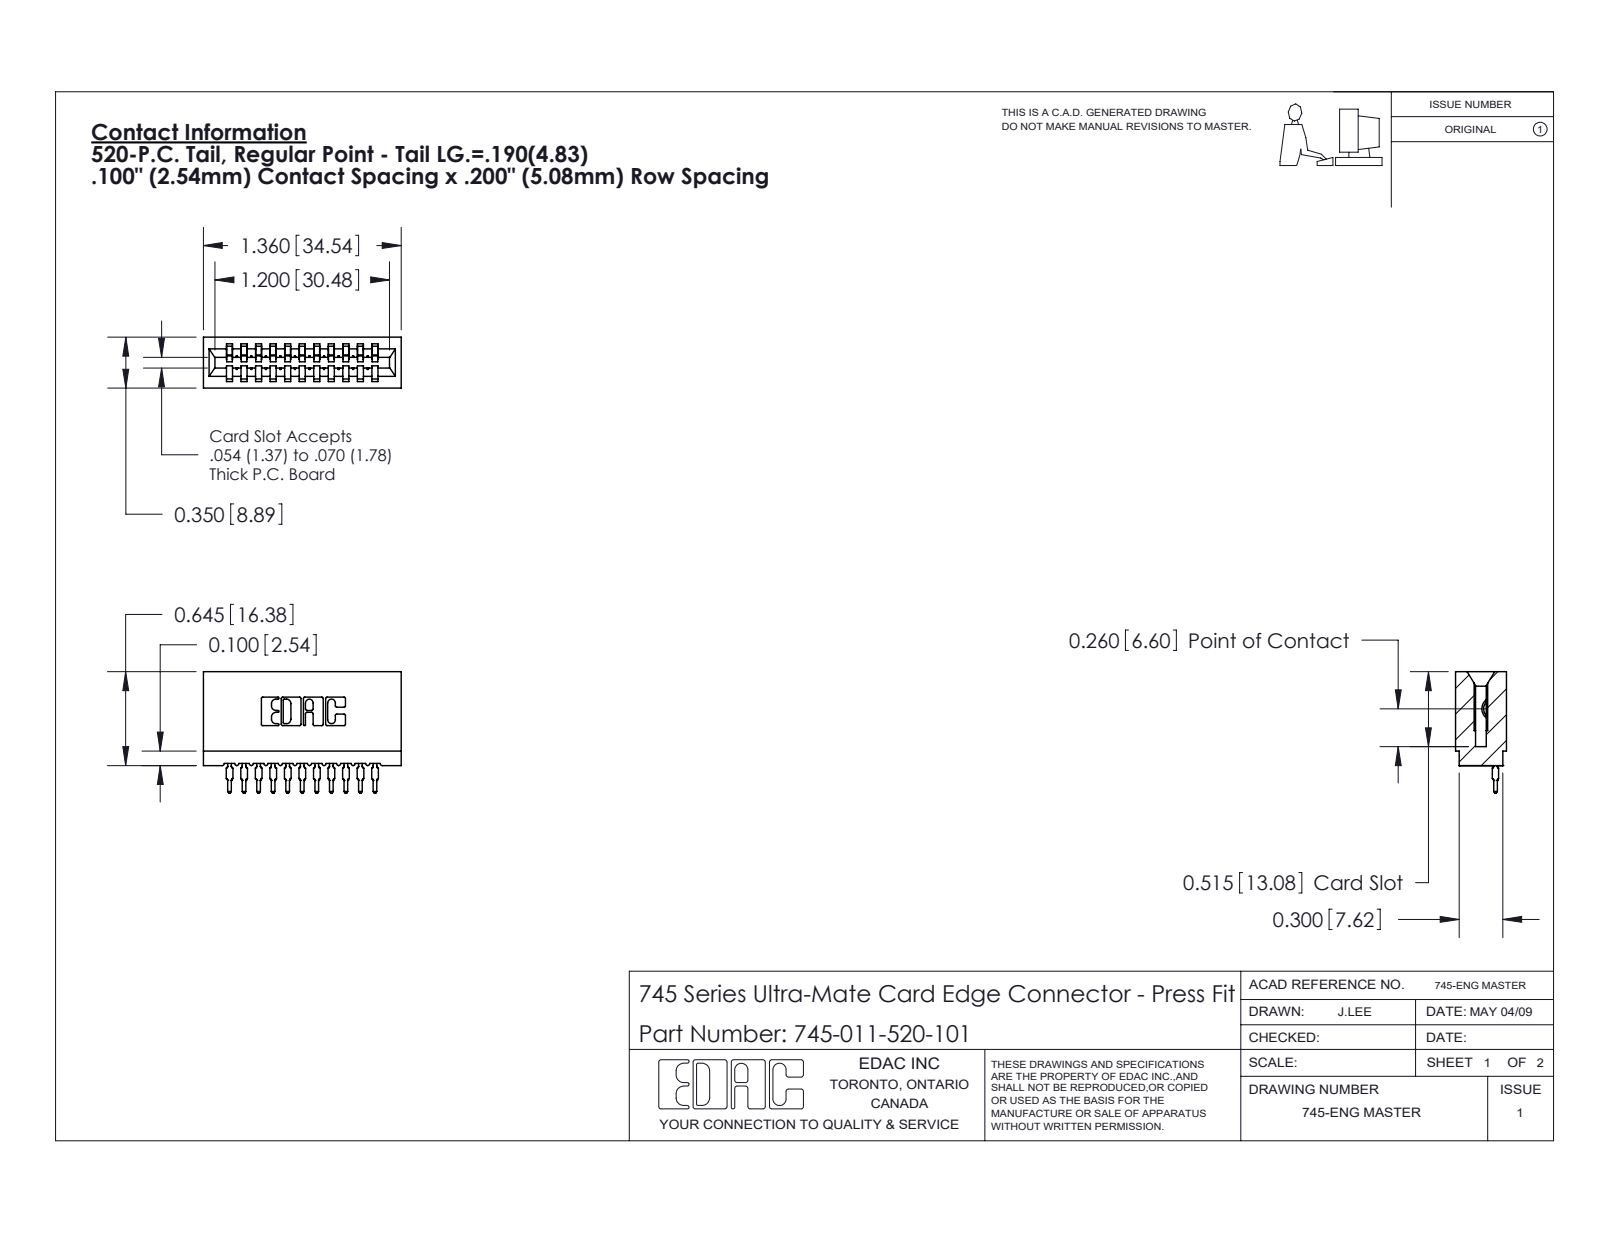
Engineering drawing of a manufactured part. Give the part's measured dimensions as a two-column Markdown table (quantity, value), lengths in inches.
| quantity | value |
| --- | --- |
| part name | 745-011-520-101; 745 Part_Insulator Option - 01; 745-292-001_520 |
| STEP written by | SolidWorks 2020 (CONFIG_CONTROL_DESIGN) |
| units | inches |
| bodies | 12 solids, 1327 faces (792 planar, 249 cylindrical, 286 other) |
| overall size | 1.36 × 0.836 × 0.35 |
| volume | 0.194 in³ |
| surface area | 8.141 in² |
| partial cylindrical surfaces (radius × count) | 0.01 × 22, 0.015 × 22, 0.021 × 22, 0.007 × 6, 0.031 × 6, 0.005 × 4, 0.011 × 4, 0.026 × 3 |
| main face-to-face distances | 0.1, 0.2, 0.3, 0.4, 0.5, 0.442, 0.342, 0.242, 0.142, 0.042 |
